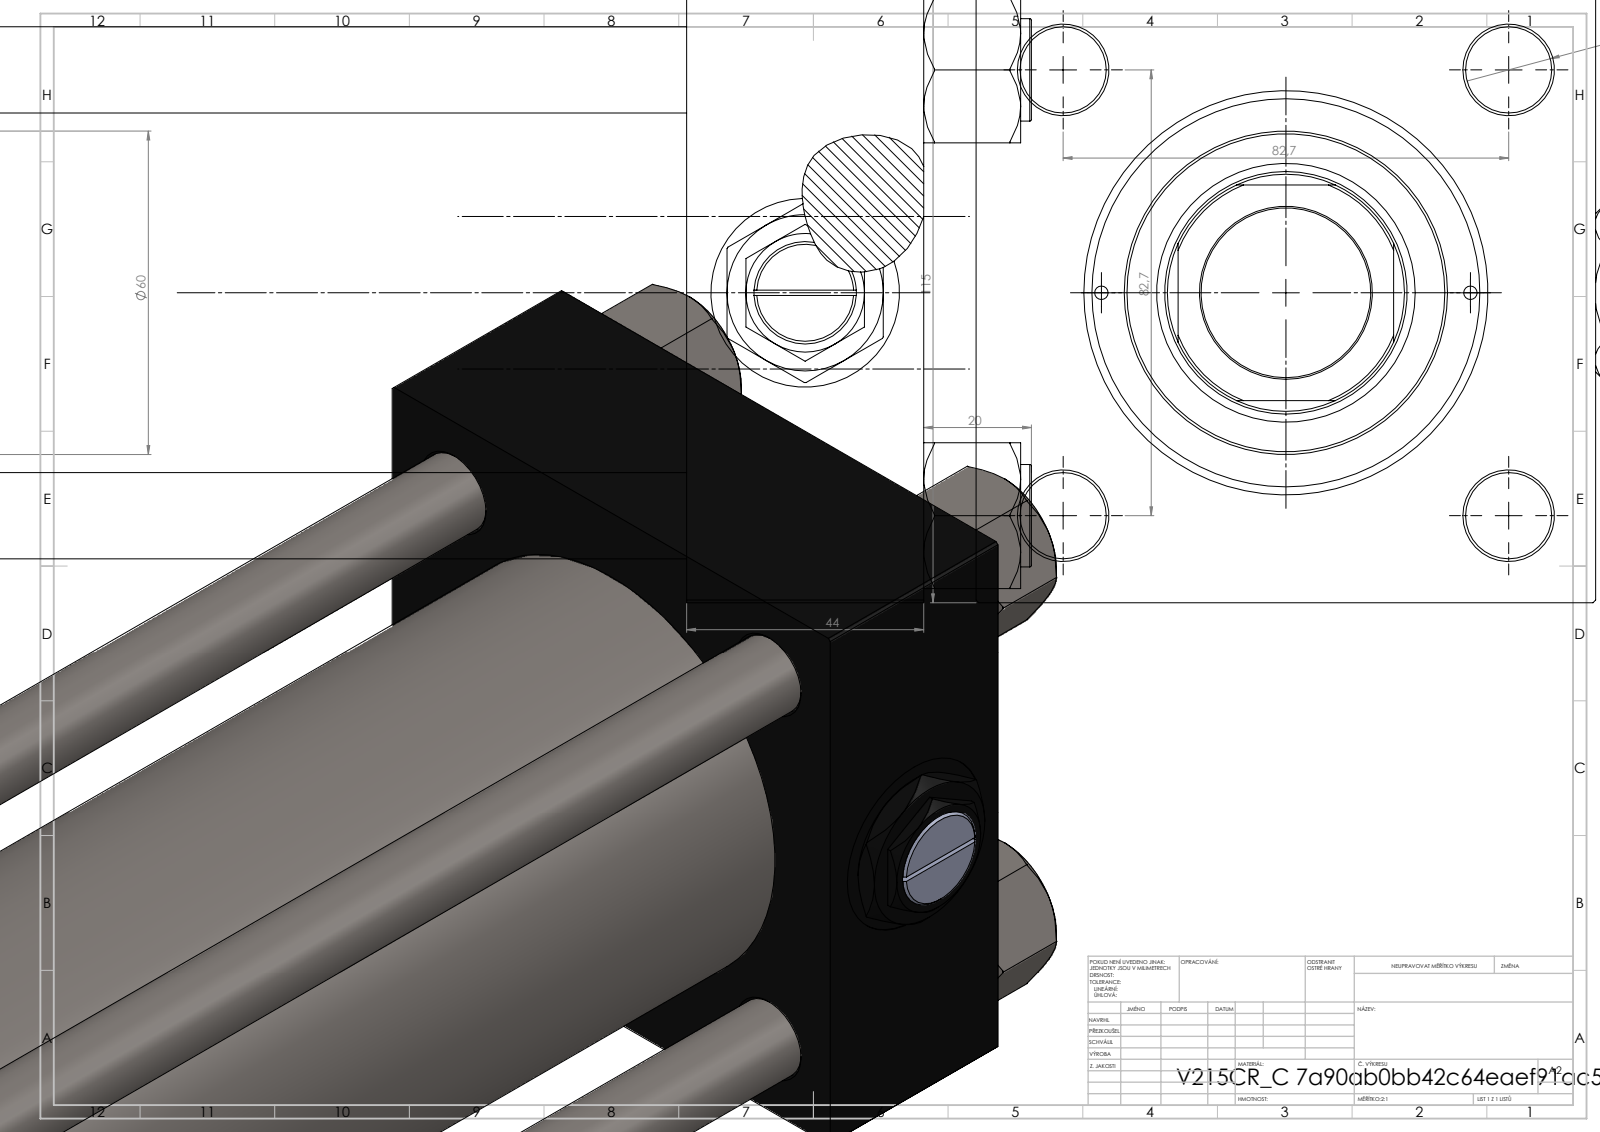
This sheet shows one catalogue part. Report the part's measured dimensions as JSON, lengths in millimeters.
{"part_name": "NUT_M5_C; V215CR_C_Body; V215_VC_A; Zatka_pro_OIL_PORT (+2 more)", "step_written_by": "SolidWorks 2019 (CONFIG_CONTROL_DESIGN)", "units": "millimeters", "bodies": {"solids": 13, "faces": 1303, "planar": 623, "cylindrical": 102, "other": 578}, "overall_size": [410, 122, 115], "volume_mm3": 2377000, "surface_area_mm2": 436380, "round_holes": [[16, 4], [2.5, 2], [7, 2], [26.44, 2], [35, 2], [31.5, 1], [45, 1], [48, 1], [61, 1], [72, 1], [80, 1]], "round_bosses_or_shafts": [[19, 4], [86, 1], [60, 1]], "partial_cylinders_radius": [[22, 1]], "face_to_face_distances": [115, 44, 359, 315, 69, 290, 246, 330.3, 286.3, 40.3], "hole_center_spacings": [41.96, 58.48, 82.7, 86.17, 34.25, 116.96, 68.5, 291]}
